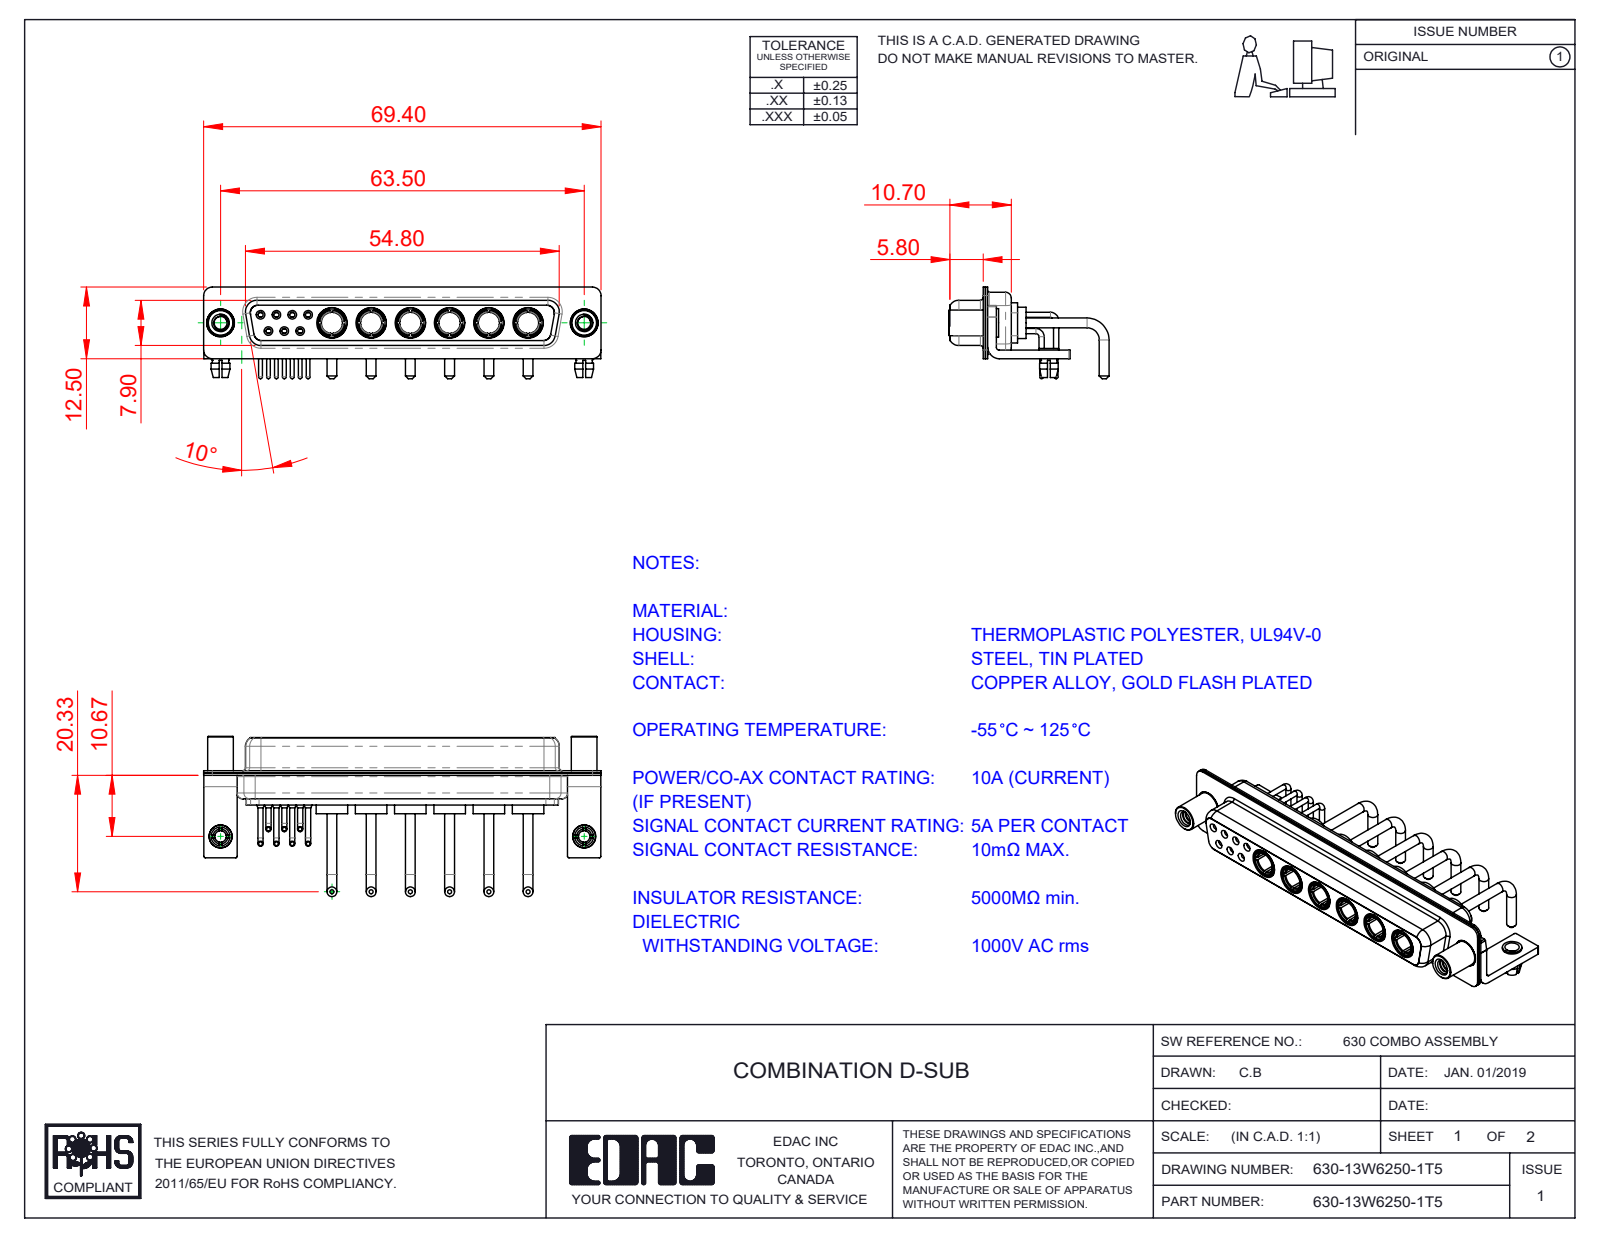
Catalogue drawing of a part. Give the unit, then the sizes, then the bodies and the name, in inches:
Units: inches
Overall size (bounding box): 2.732 × 1.102 × 0.63
Round holes (diameter × count): ⌀0.079 ×9, ⌀0.191 ×8, ⌀0.035 ×7, ⌀0.043 ×7, ⌀0.059 ×7, ⌀0.146 ×6, ⌀0.209 ×6, ⌀0.067 ×4, ⌀0.063 ×3, ⌀0.089 ×2, ⌀0.098 ×2, ⌀0.126 ×2
Round bosses / shafts (diameter × count): ⌀0.067 ×12, ⌀0.035 ×7, ⌀0.026 ×7, ⌀0.217 ×6, ⌀0.205 ×6, ⌀0.195 ×6, ⌀0.187 ×6, ⌀0.148 ×6
Partial cylindrical surfaces — rounded edges, fillets, slot ends (radius × count): R0.01 ×16, R0.059 ×16, R0.079 ×13, R0.053 ×8, R0.063 ×8, R0.083 ×6, R0.02 ×5, R0.024 ×4
Main face-to-face distances: 0.016, 0.018, 0.055, 0.333, 0.071, 0.35, 0.278, 0.244, 0.295, 0.059
Hole centre spacings: 0.124, 0.109, 0.27, 0.539, 0.218, 0.809, 0.198, 0.198
Volume: 0.358 in³ · Surface area: 20.58 in²
Bodies: 28 solids, 1298 faces (416 planar, 540 cylindrical, 342 other)
Part name (STEP PRODUCT): 630-13W6250-1T5; 630Combo Contact Row 2; 630Combo Shell Rear_37 Contacts; Power Socket_Ext 10A RA (+6 more)
STEP written by: SolidWorks 2020 (CONFIG_CONTROL_DESIGN)
